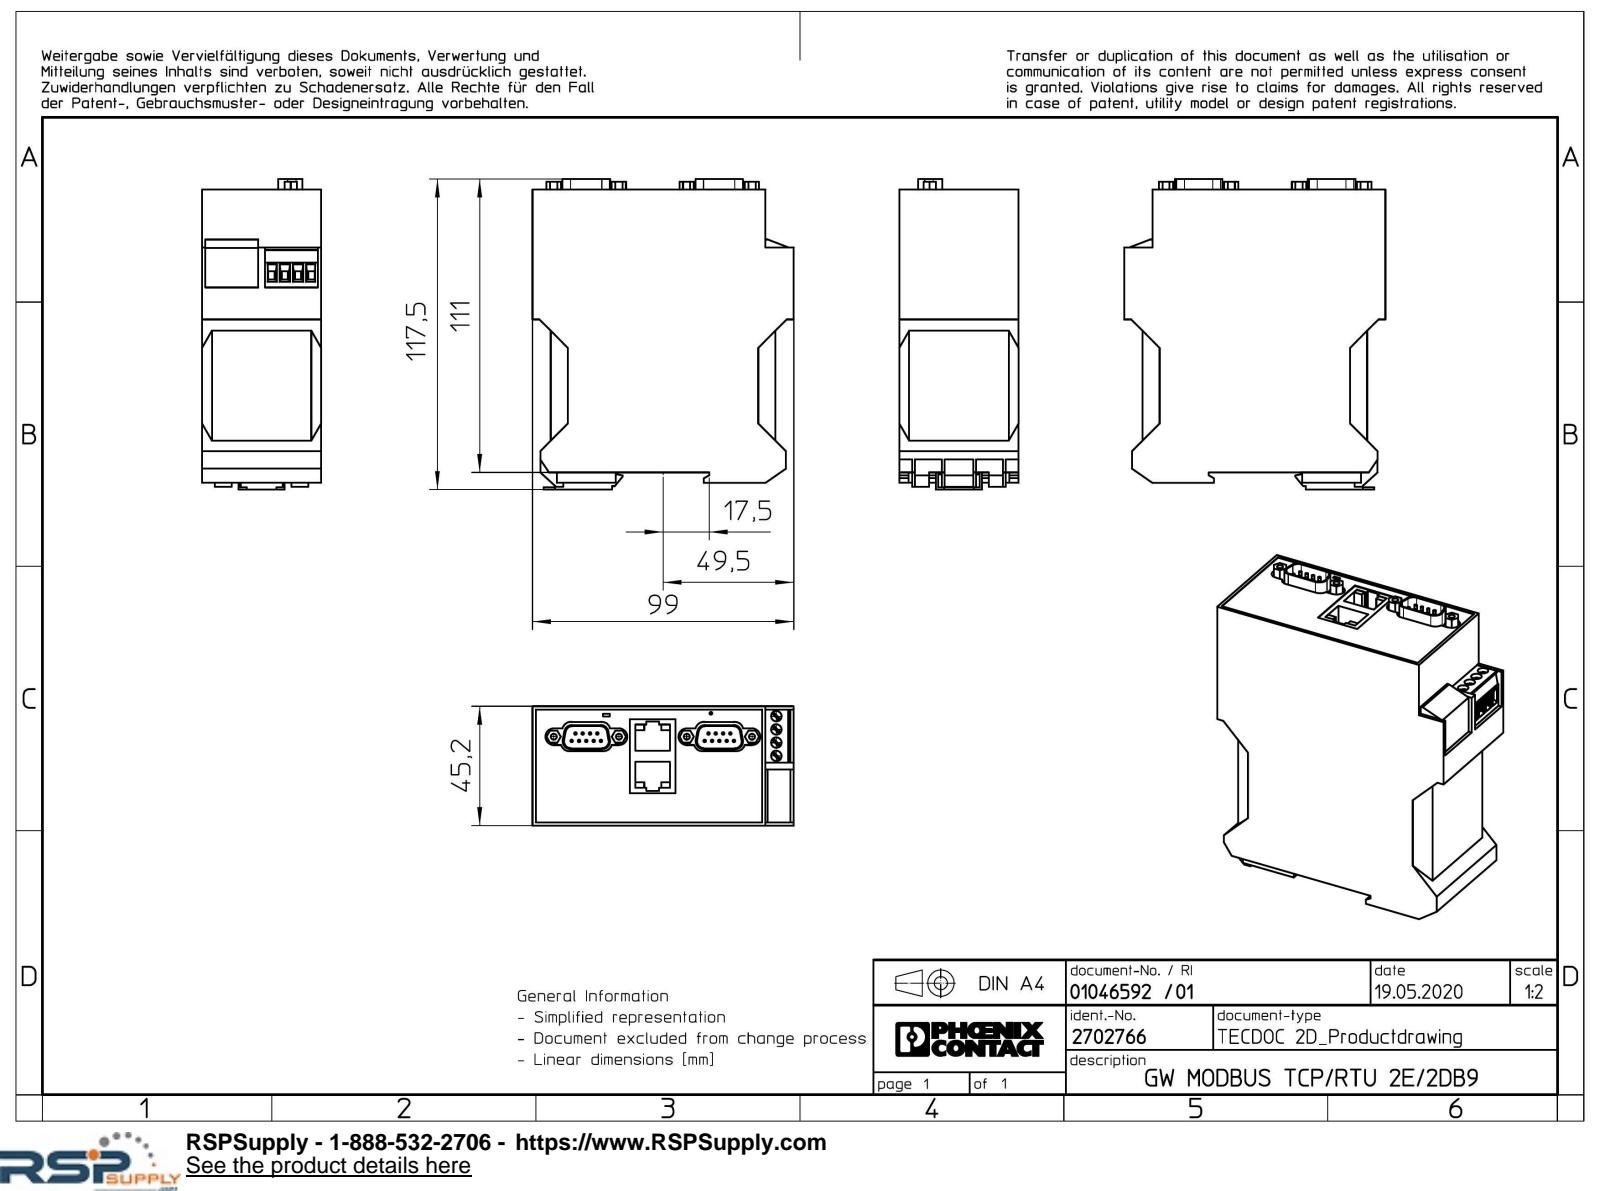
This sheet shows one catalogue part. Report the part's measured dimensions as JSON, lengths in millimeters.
{"part_name": "GW_MODBUS_TCP_RTU_2E_2DB9-select", "step_written_by": "Creo Elements/Direct Modeling 20.1A 29-Sep-2018 (C) Parametric Technology GmbH (AUTOMOTIVE_DESIGN)", "units": "millimeters", "bodies": {"solids": 1, "faces": 412, "planar": 330, "cylindrical": 82, "other": 0}, "overall_size": [117.5, 99, 45.2], "volume_mm3": 437570, "surface_area_mm2": 43514, "round_holes": [[2.29, 4], [4, 4], [1.08, 1]], "round_bosses_or_shafts": [[1, 18]], "partial_cylinders_radius": [[3.17, 12], [2.54, 8], [3.04, 8]], "face_to_face_distances": [45.2, 92.05, 6.95, 4, 106.8, 85.1, 110.8, 3.75, 88.3, 81.35], "hole_center_spacings": [5, 10, 24.74, 50.4, 9.48, 9.6, 11.73, 12.02]}
